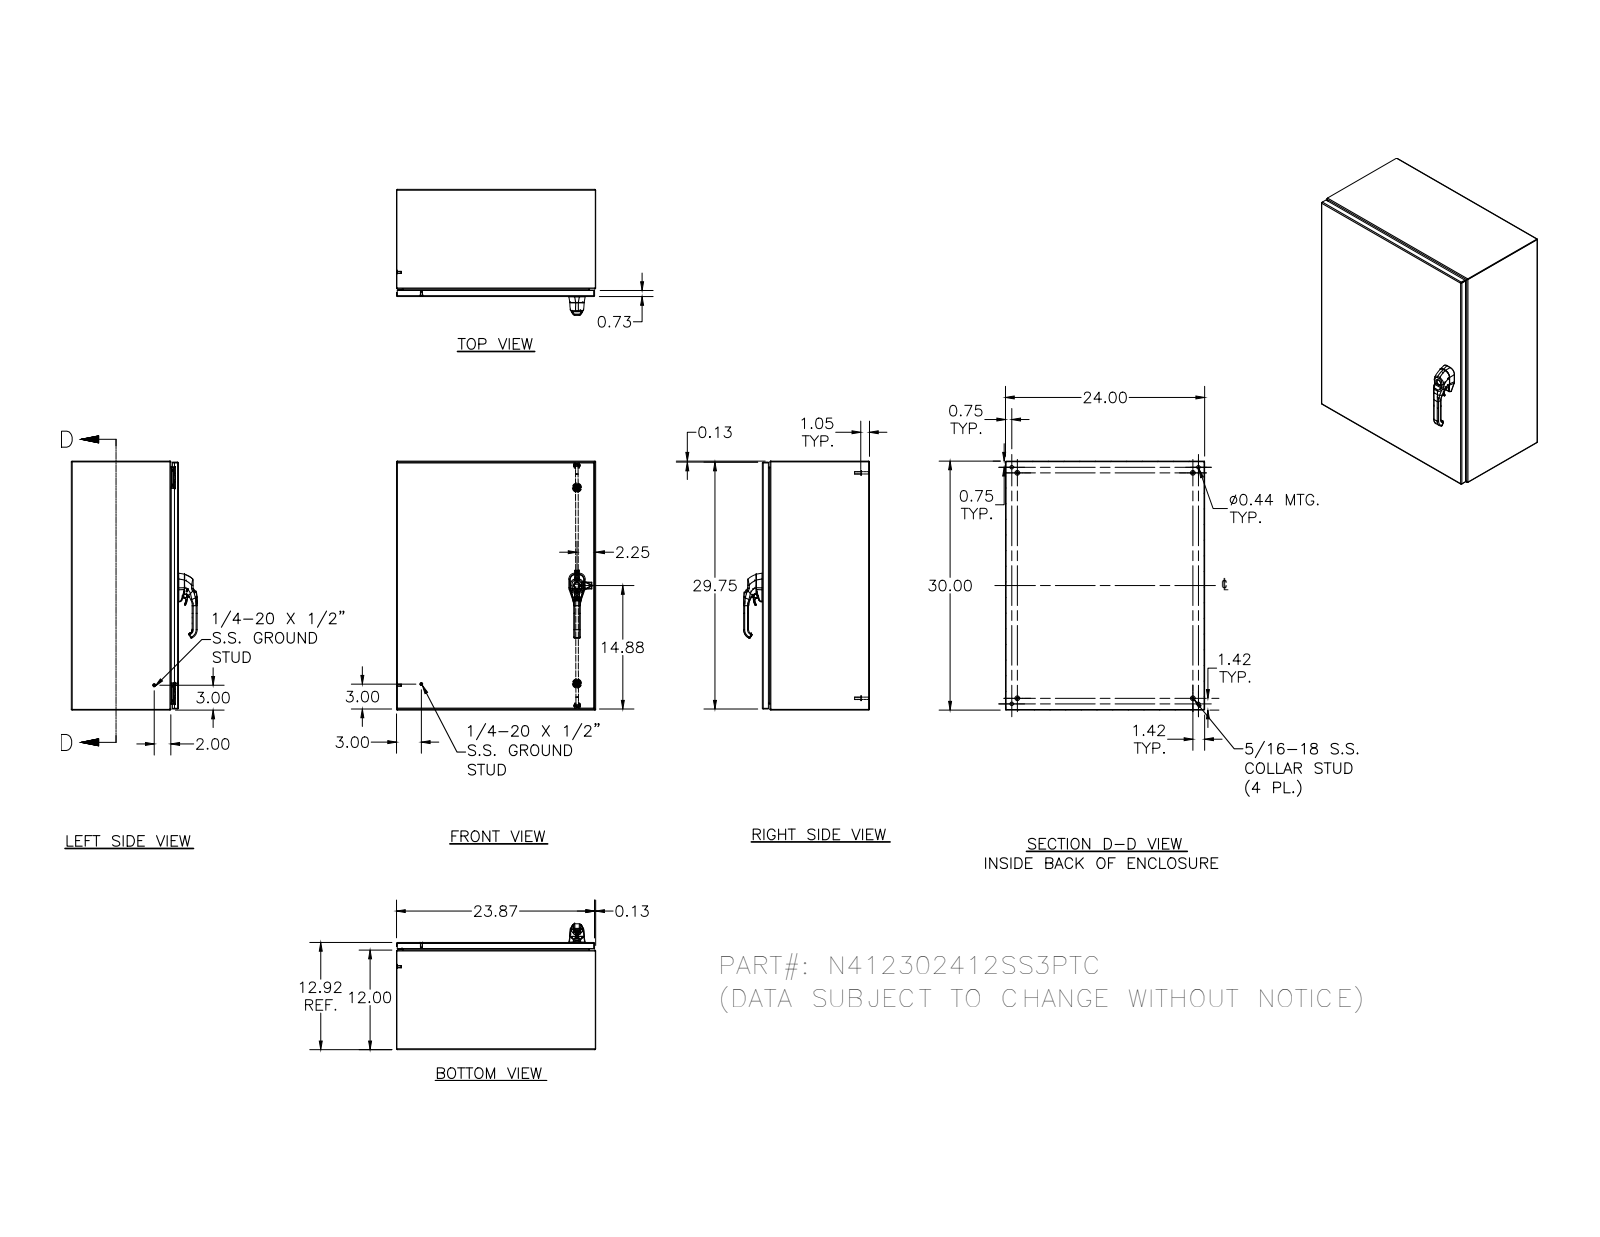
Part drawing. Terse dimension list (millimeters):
name: N412302412SS3PTC; N412302412SS3PTCBKP; N4123024SS3PTCLID; HFW328176 (+8 more)
written by: Autodesk Inventor 2011 (AUTOMOTIVE_DESIGN)
unit: mm
bodies: 63 solids, 3086 faces (1046 planar, 1117 cylindrical, 923 other)
size: 762 × 609.6 × 385.2
volume: 3 754 000 mm³; area: 3 914 000 mm²
holes: 5× ⌀4.2, 4× ⌀2.4, 4× ⌀3.9, 4× ⌀4.2, 4× ⌀4.4, 4× ⌀4.8, 4× ⌀5, 4× ⌀11.1, 3× ⌀5.4, 2× ⌀2.7, 2× ⌀4, 2× ⌀4.1
bosses: 10× ⌀6.4, 6× ⌀6, 4× ⌀15, 4× ⌀14.3, 4× ⌀9.1, 4× ⌀8.1, 4× ⌀7.9, 4× ⌀7.6
rounds: 180× R0.5, 101× R0.3, 30× R0.8, 26× R1.3, 23× R3, 21× R0.5, 20× R2.7, 18× R0.4
face distances: 1.9, 326.2, 607.7, 328.1, 324.3, 760.1, 605.8, 609.6, 762, 758.2
hole spacings: 660.3, 580.9, 0.4, 16.8, 41.1, 677.1, 0.5, 12.7
